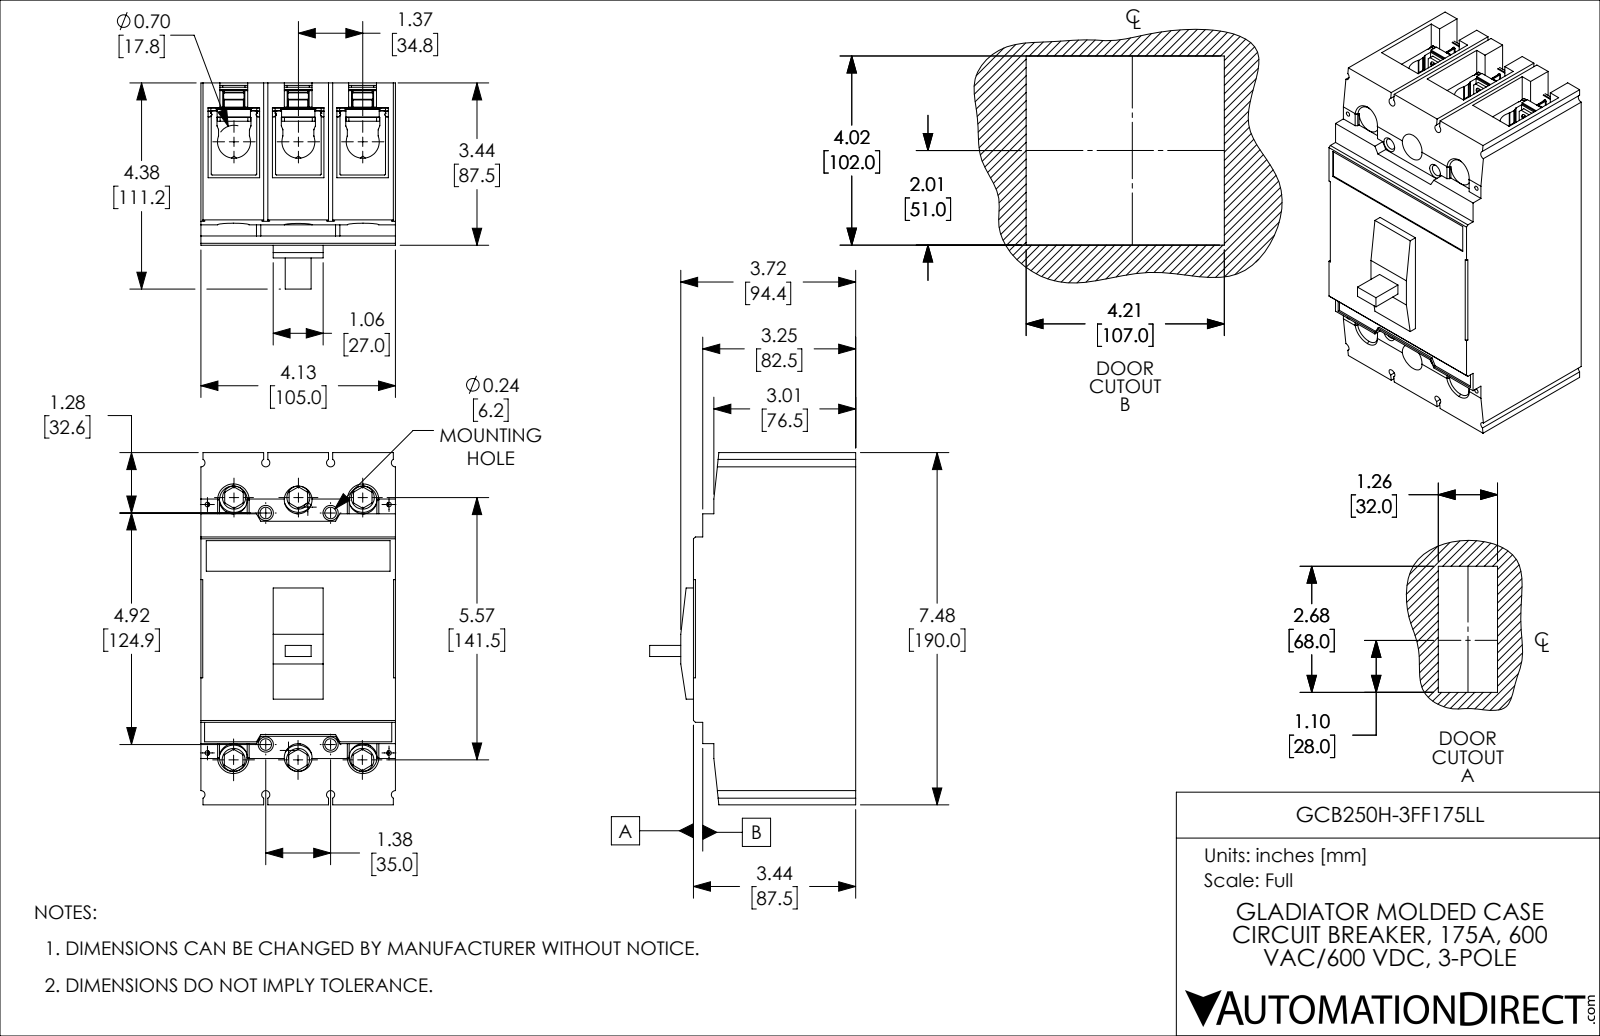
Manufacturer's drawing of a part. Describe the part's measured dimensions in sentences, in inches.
The part is named "GCB250H-3FF175LL". Its 3-D file was written by "SolidWorks 2021 (CONFIG_CONTROL_DESIGN)". It is 25 solids with 2233 faces: 975 planar, 958 cylindrical and 300 other. Overall it measures 7.48 by 4.378 by 4.134 inches. Its volume is 87.11 cubic inches and its surface area 315.7 square inches. Round holes: 24 of diameter 0.067, 24 of diameter 0.157, 10 of diameter 0.098, 6 of diameter 0.354, 6 of diameter 0.591, 6 of diameter 0.689, 4 of diameter 0.173, 4 of diameter 0.244. Round bosses or shafts: 6 of diameter 0.709. Partial cylindrical surfaces (rounded edges, fillets, slot ends): 206 of radius 0.012, 72 of radius 0.039, 36 of radius 0.059, 26 of radius 0.02, 24 of radius 0.008, 20 of radius 0.079, 12 of radius 0.016, 12 of radius 0.031. The main face-to-face distances are 1.368, 4.134, 2.736, 1.094, 0.843, 0.252, 0.059, 1.378, 6.102, 3.445. The hole center spacings are 0.285, 0.743, 1.046, 1.378, 5.24, 6.298, 1.368, 1.426.
